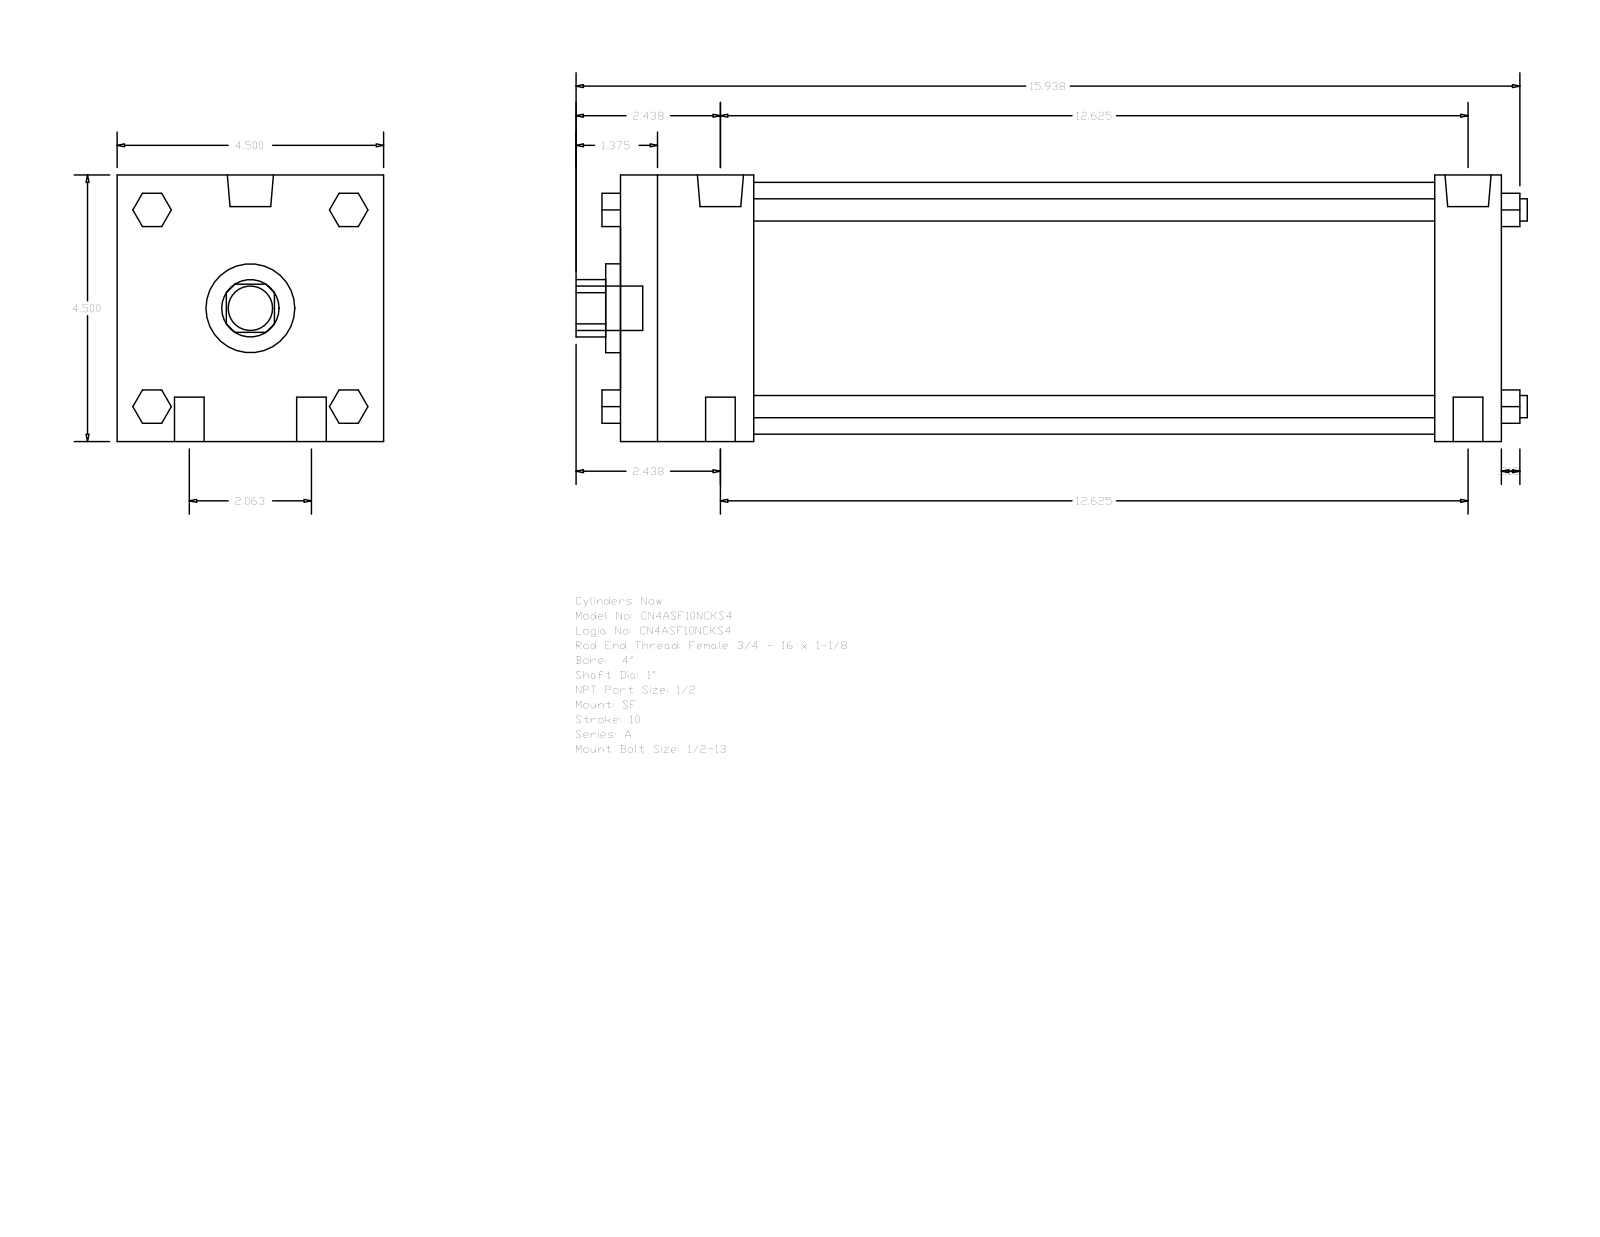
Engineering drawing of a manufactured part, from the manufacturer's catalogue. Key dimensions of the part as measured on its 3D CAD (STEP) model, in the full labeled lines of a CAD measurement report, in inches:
Part name (STEP PRODUCT): A_SF__0400_1
STEP written by: GSSL Pune (CONFIG_CONTROL_DESIGN)
Units: inches
Bodies: 0 solids, 124 faces (94 planar, 30 cylindrical, 0 other)
Overall size (bounding box): 16.063 × 4.5 × 4.5
Round holes (diameter × count): ⌀1 ×1, ⌀1.5 ×1, ⌀4.25 ×1
Round bosses / shafts (diameter × count): ⌀0.5 ×4, ⌀0.375 ×4, ⌀0.778 ×2, ⌀0.344 ×2, ⌀0.75 ×1
Partial cylindrical surfaces — rounded edges, fillets, slot ends (radius × count): R0.484 ×1
Main face-to-face distances: 4.5, 14.875, 13.75, 1.125, 2.25, 11.5, 12.625, 0.563, 1.66, 2.875
